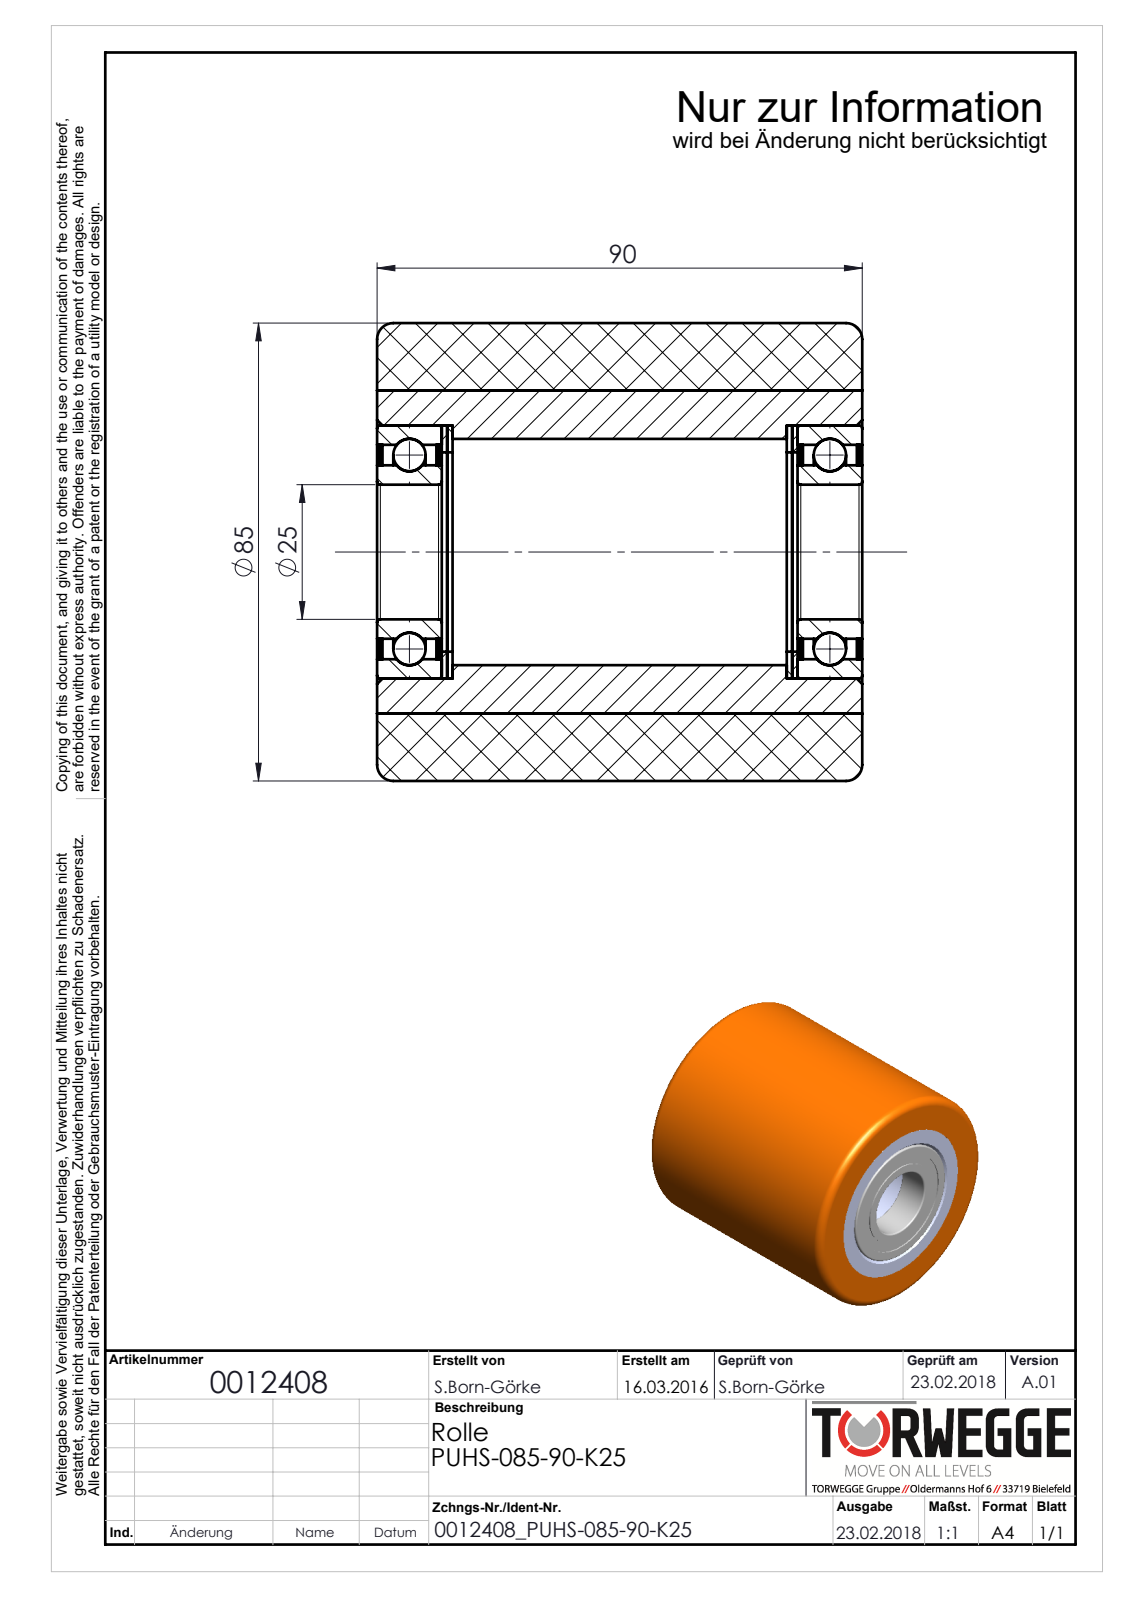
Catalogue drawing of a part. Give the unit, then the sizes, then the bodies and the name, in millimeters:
Units: millimetres
Overall size (bounding box): 90 × 85 × 85
Round holes (diameter × count): ⌀25 ×1, ⌀32.2 ×1, ⌀37 ×1, ⌀39.8 ×1, ⌀42 ×1, ⌀60 ×1
Round bosses / shafts (diameter × count): ⌀85 ×1, ⌀47 ×1
Main face-to-face distances: 1, 78, 90, 12, 0.5, 13, 77, 65, 64, 76
Volume: 402 553 mm³ · Surface area: 106 559 mm²
Bodies: 16 solids, 158 faces (30 planar, 68 cylindrical, 60 other)
Part name (STEP PRODUCT): 0012408_PUHS-085-90-K25
STEP written by: SolidWorks 2016 (AUTOMOTIVE_DESIGN)
